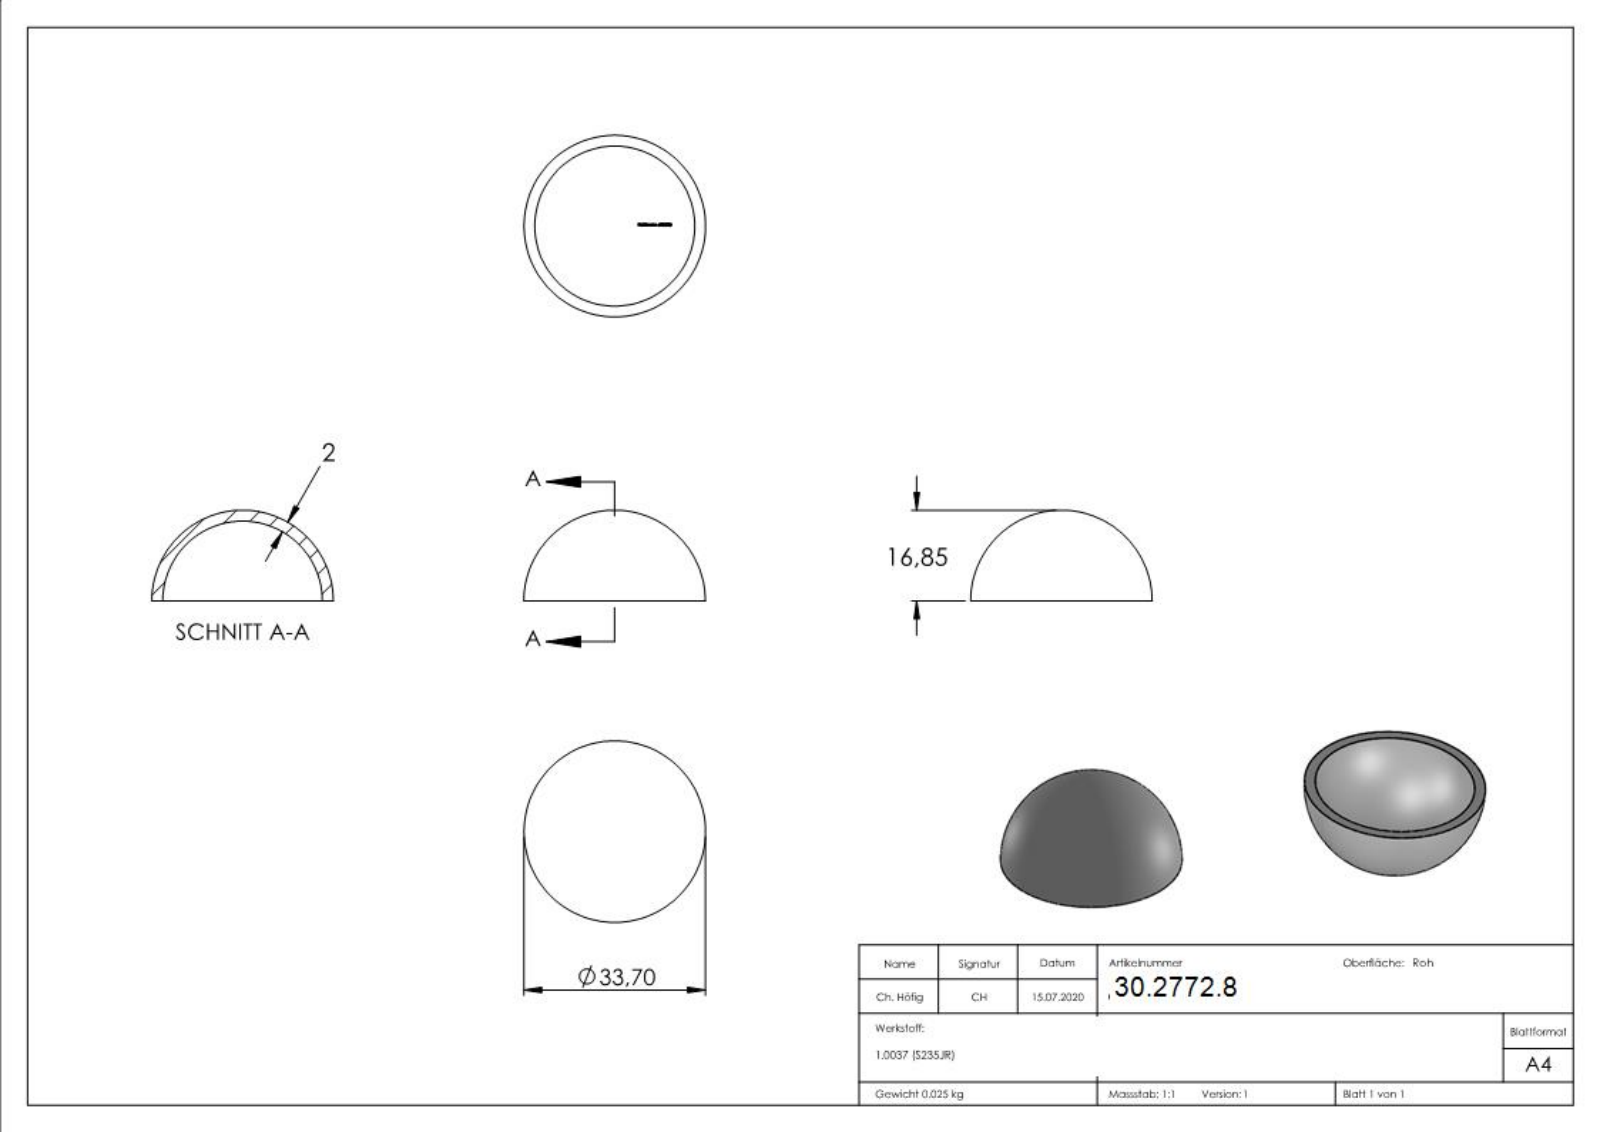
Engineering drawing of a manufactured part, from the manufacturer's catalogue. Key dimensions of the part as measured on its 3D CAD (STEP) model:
Part name (STEP PRODUCT): 620033
STEP written by: SolidWorks 2018 (CONFIG_CONTROL_DESIGN)
Units: millimetres
Bodies: 1 solid, 201 faces (70 planar, 0 cylindrical, 131 other)
Overall size (bounding box): 33.7 × 33.7 × 16.85
Volume: 3 161 mm³ · Surface area: 3 373 mm²
Main face-to-face distances: 0.45, 0.5, 0.61, 1.19, 0.55, 0.81, 0.85, 1.31, 0.4, 0.53
